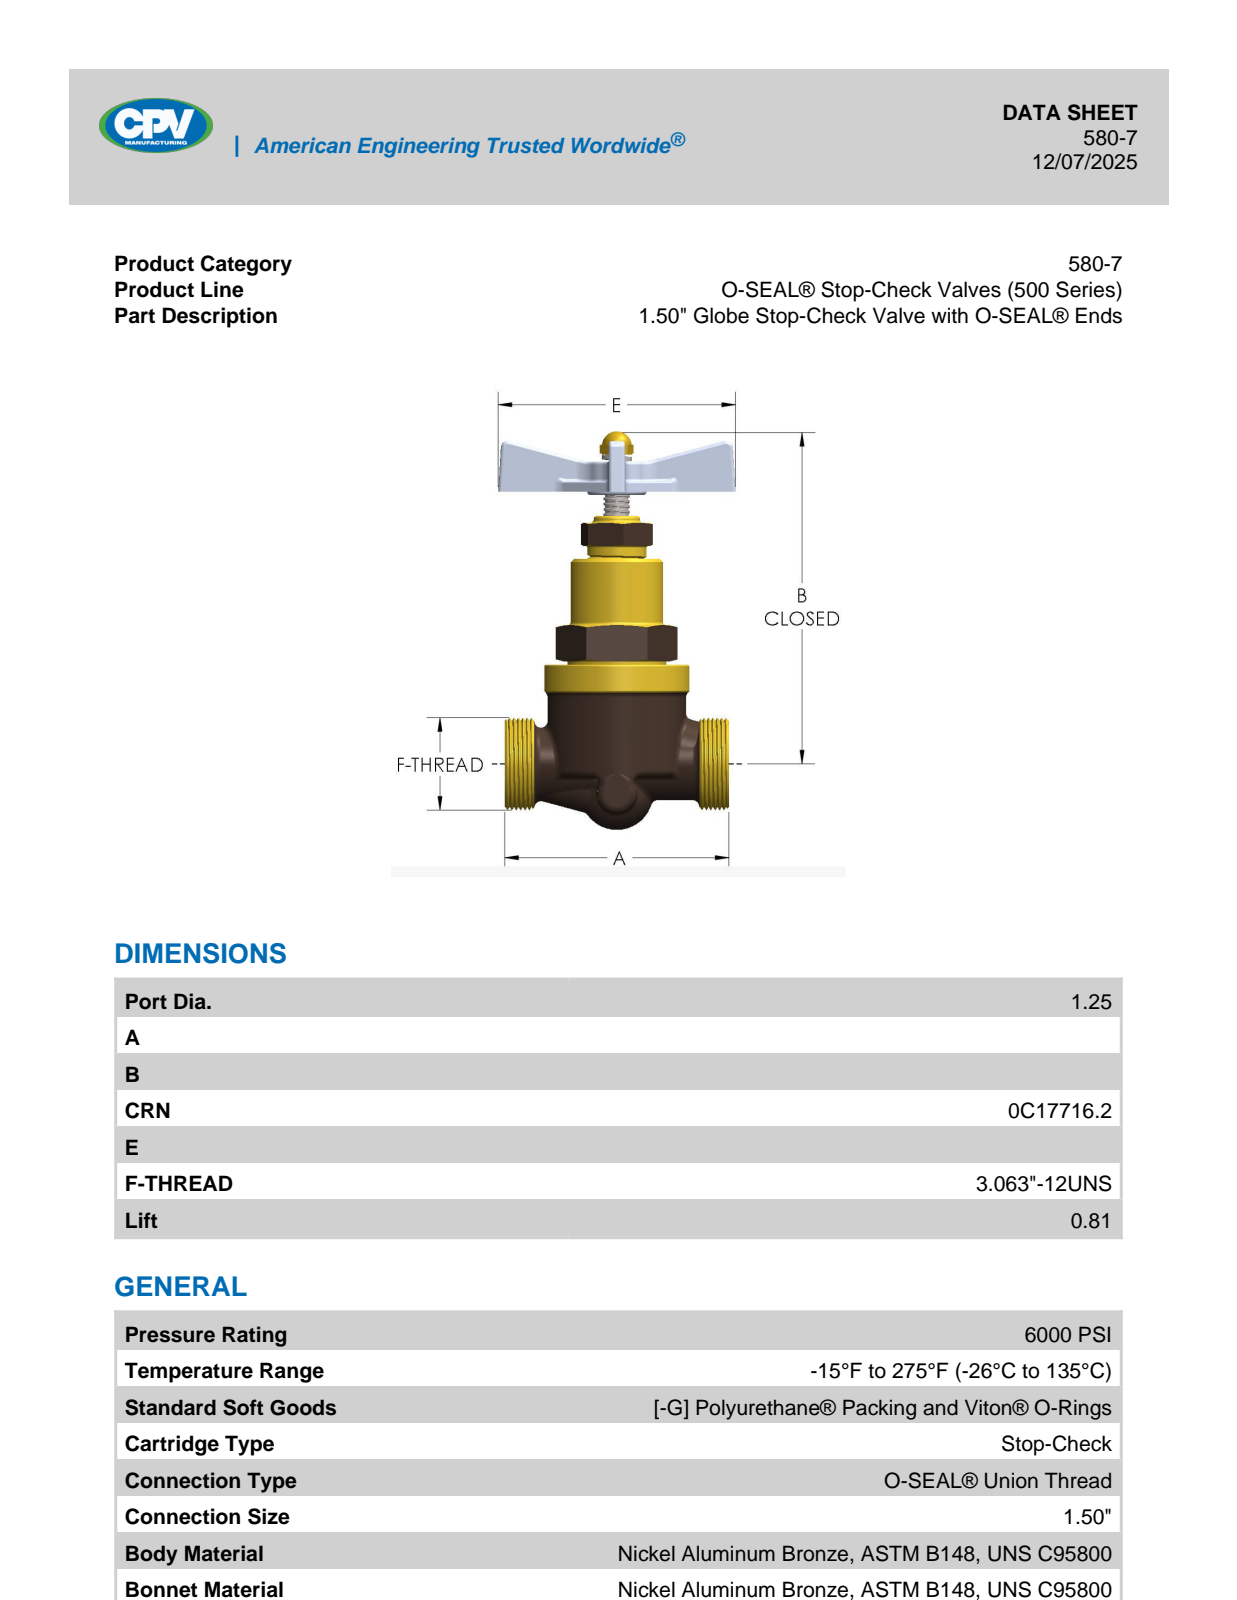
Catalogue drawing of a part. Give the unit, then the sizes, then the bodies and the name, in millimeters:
Units: millimetres
Overall size (bounding box): 319.5 × 292.1 × 149.4
Round holes (diameter × count): ⌀31.8 ×3, ⌀12.9 ×1, ⌀48.5 ×1, ⌀88.9 ×1, ⌀90.4 ×1
Round bosses / shafts (diameter × count): ⌀77.8 ×2, ⌀44.5 ×2, ⌀149.4 ×1, ⌀142.9 ×1, ⌀88.8 ×1, ⌀82.8 ×1, ⌀82.6 ×1, ⌀76.2 ×1
Partial cylindrical surfaces — rounded edges, fillets, slot ends (radius × count): R3.3 ×14, R0.8 ×12, R12.7 ×2, R11 ×1, R31.2 ×1, R40.2 ×1, R53.2 ×1, R74.5 ×1
Main face-to-face distances: 92.2, 114.3, 16, 24.1, 90.2, 19.8, 4.3, 94.5, 233.5, 6.4
Hole centre spacings: 47.6
Volume: 2 863 000 mm³ · Surface area: 279 900 mm²
Bodies: 1 solid, 681 faces (135 planar, 304 cylindrical, 242 other)
Part name (STEP PRODUCT): 380-7
STEP written by: SolidWorks 2018 (AUTOMOTIVE_DESIGN)
